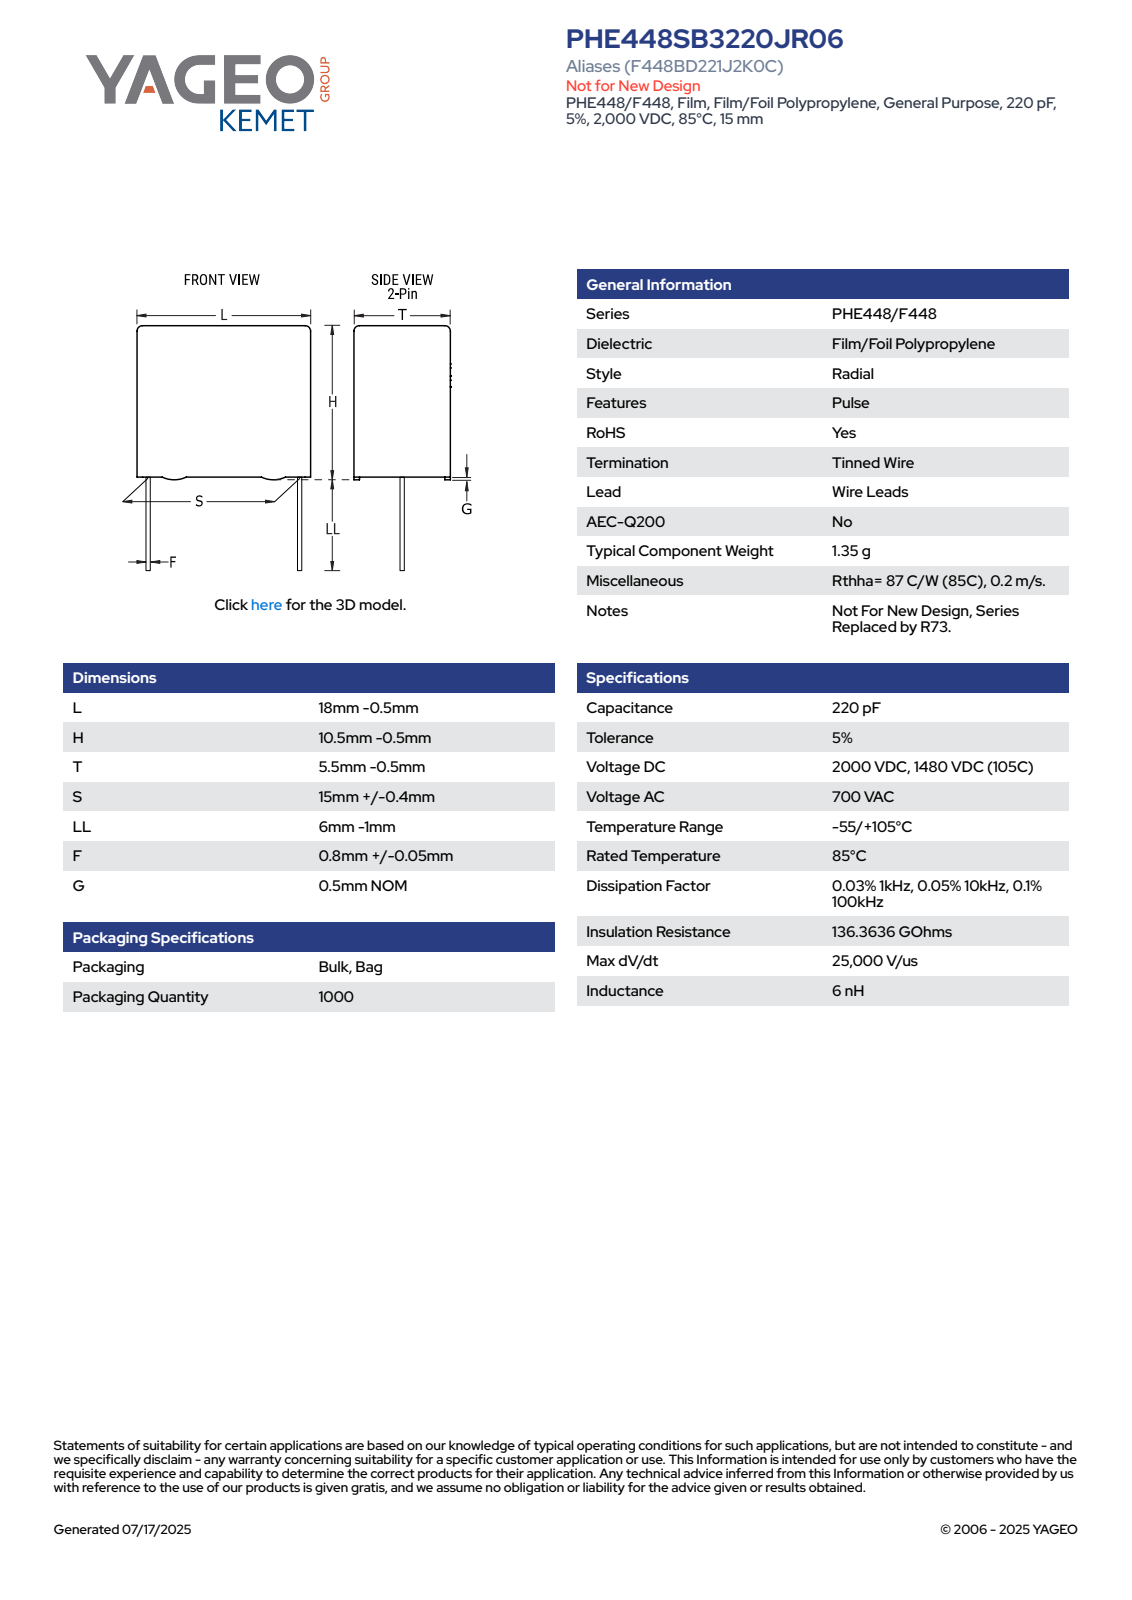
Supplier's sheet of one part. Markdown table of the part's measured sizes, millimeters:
| quantity | value |
| --- | --- |
| part name | CFR_RBG_18X10.5X5.5_L17.5H10T5S15LL5F0.85G0.5 |
| STEP written by | SolidWorks 2020 (AUTOMOTIVE_DESIGN) |
| units | millimeters |
| bodies | 4 solids, 89 faces (81 planar, 8 cylindrical, 0 other) |
| overall size | 17.5 × 15 × 5 |
| volume | 837 mm³ |
| surface area | 667 mm² |
| round bosses / shafts (diameter × count) | 0.85 × 2 |
| partial cylindrical surfaces (radius × count) | 0.5 × 4 |
| main face-to-face distances | 5, 9.5, 17.5, 0.5, 10, 4.72, 4.43, 4.71, 5.5, 15 |
